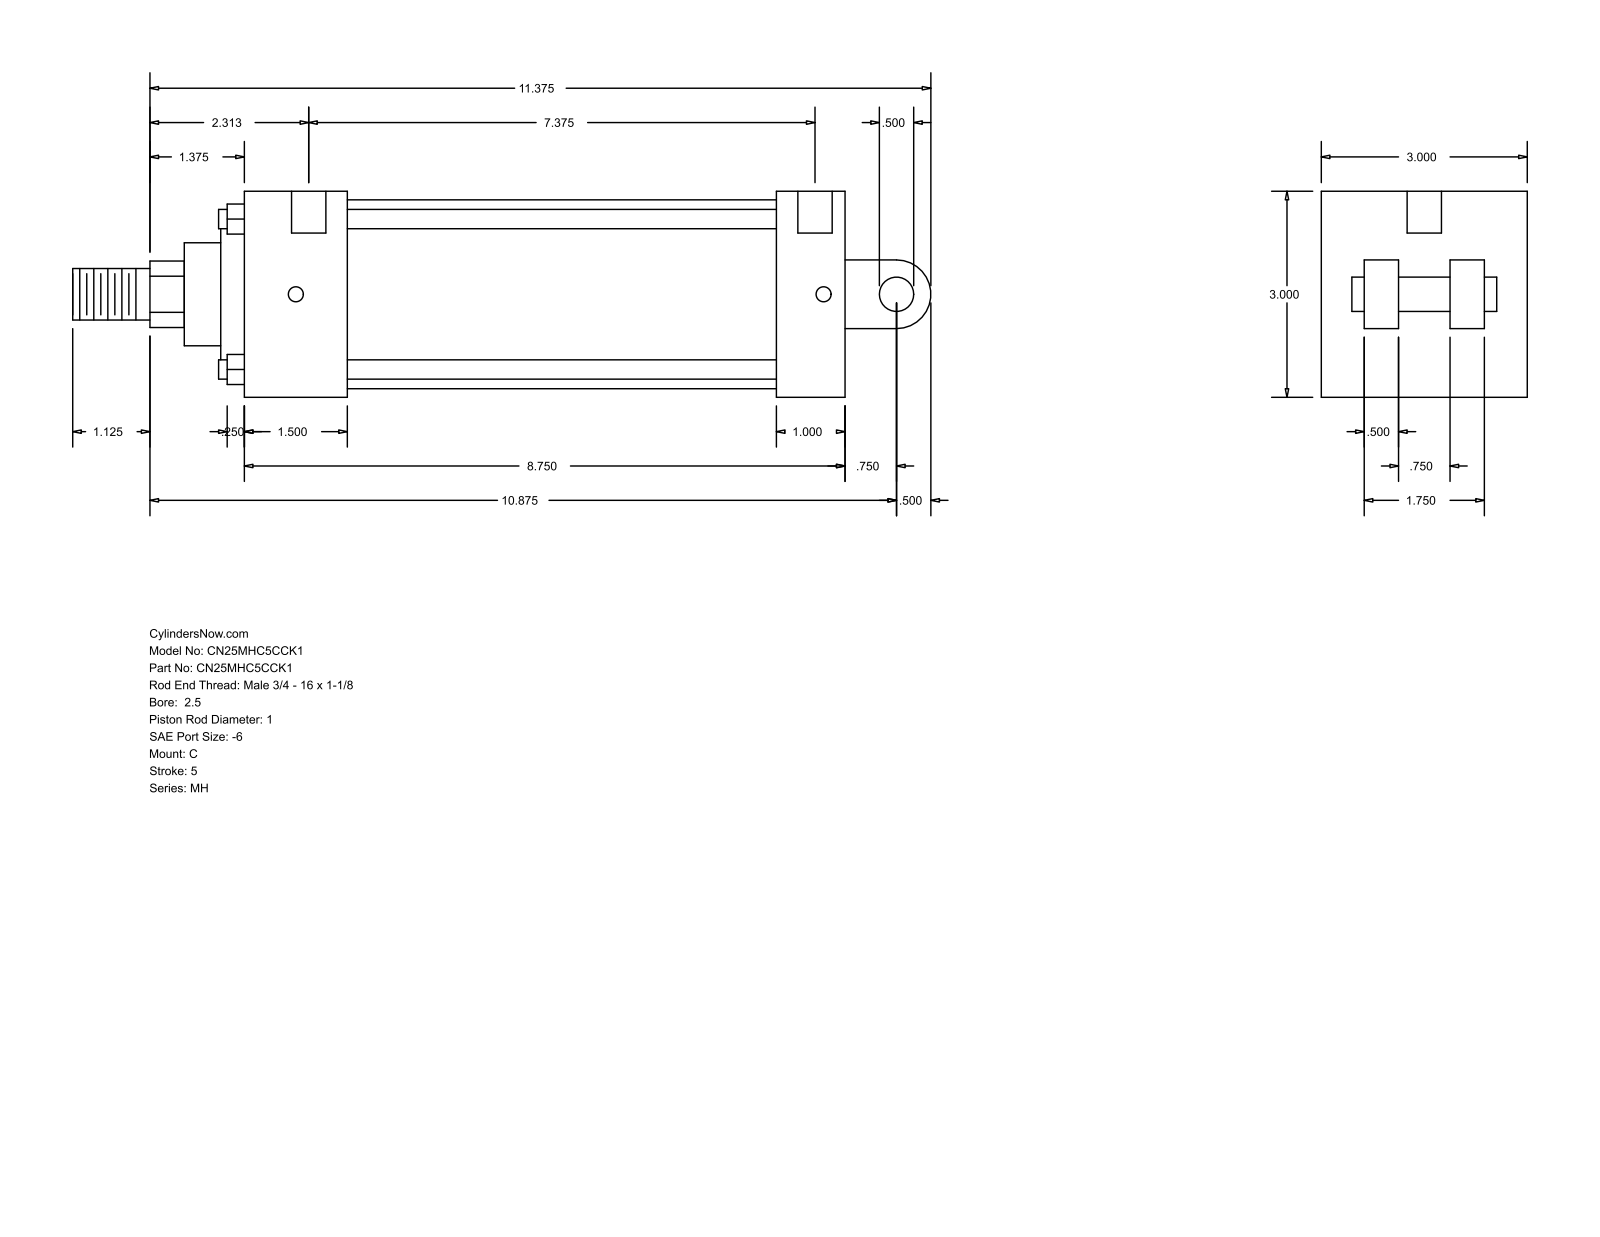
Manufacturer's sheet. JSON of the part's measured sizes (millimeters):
{"part_name": "MH_C__0250_1", "step_written_by": "GSSL Pune (CONFIG_CONTROL_DESIGN)", "units": "millimeters", "bodies": {"solids": 0, "faces": 101, "planar": 71, "cylindrical": 30, "other": 0}, "overall_size": [317.5, 76.2, 76.2], "round_holes": [[5.56, 4], [12.7, 2]], "round_bosses_or_shafts": [[7.14, 4], [69.85, 1], [60.33, 1], [38.1, 1], [25.4, 1], [19.05, 1], [12.7, 1]], "partial_cylinders_radius": [[12.29, 1], [12.7, 1]], "face_to_face_distances": [76.2, 25.4, 222.26, 60.33, 15.87, 196.86, 38.11, 158.75, 184.15, 12.7], "hole_center_spacings": [195.26, 3.18, 4.76, 187.32, 190.5, 192.08]}
